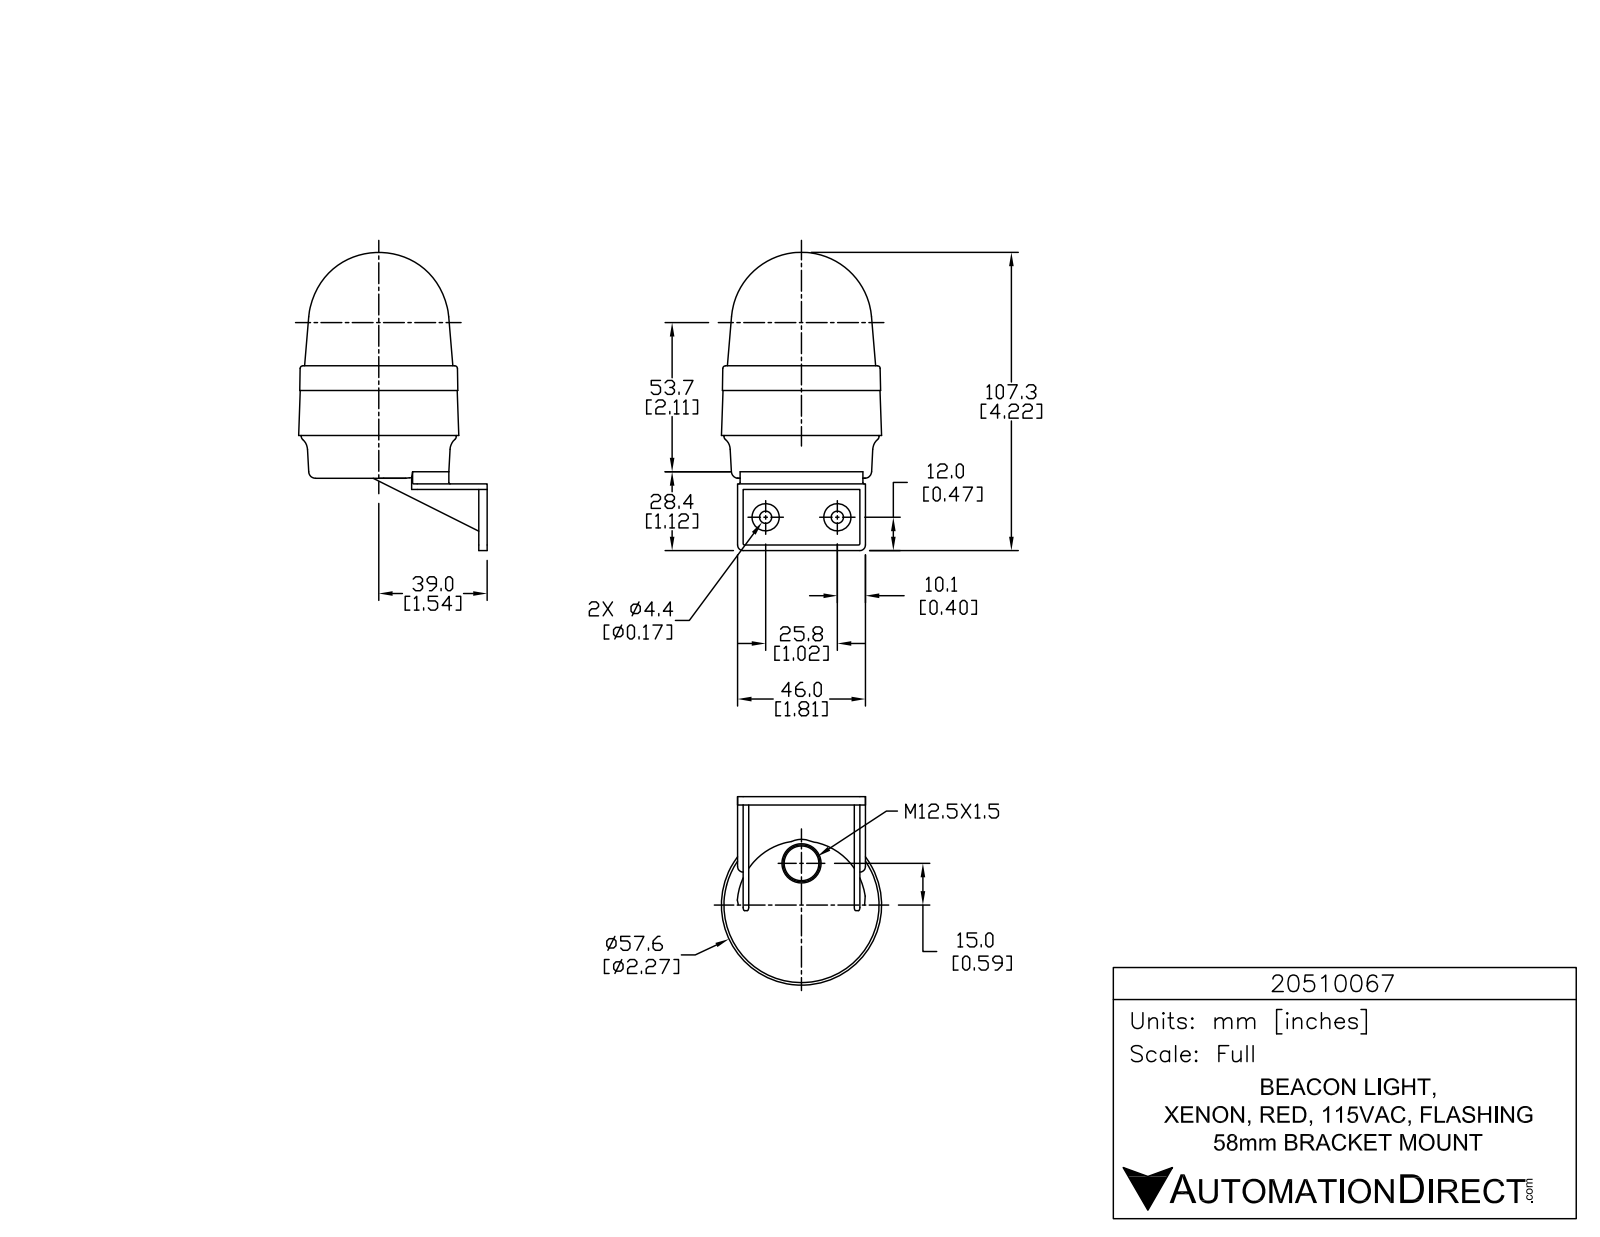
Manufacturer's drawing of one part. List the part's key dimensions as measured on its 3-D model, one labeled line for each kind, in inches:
Part name (STEP PRODUCT): 20510067
STEP written by: SolidWorks 2015 (AUTOMOTIVE_DESIGN)
Units: inches
Bodies: 1 solid, 828 faces (551 planar, 179 cylindrical, 98 other)
Overall size (bounding box): 4.225 × 2.852 × 2.407
Volume: 10.27 in³ · Surface area: 33.38 in²
Round holes (diameter × count): ⌀0.039 ×3, ⌀0.173 ×2
Round bosses / shafts (diameter × count): ⌀0.226 ×3, ⌀0.056 ×3, ⌀0.386 ×2, ⌀2.197 ×1
Partial cylindrical surfaces — rounded edges, fillets, slot ends (radius × count): R0.008 ×6, R0.008 ×6, R0.008 ×6, R0.02 ×6, R0.131 ×6, R0.079 ×4, R0.004 ×3, R0.005 ×3
Main face-to-face distances: 0.079, 0.157, 1.575, 1.654, 0.039, 0.118, 1.496, 0.866, 0.945, 0.764
Hole centre spacings: 1.016
